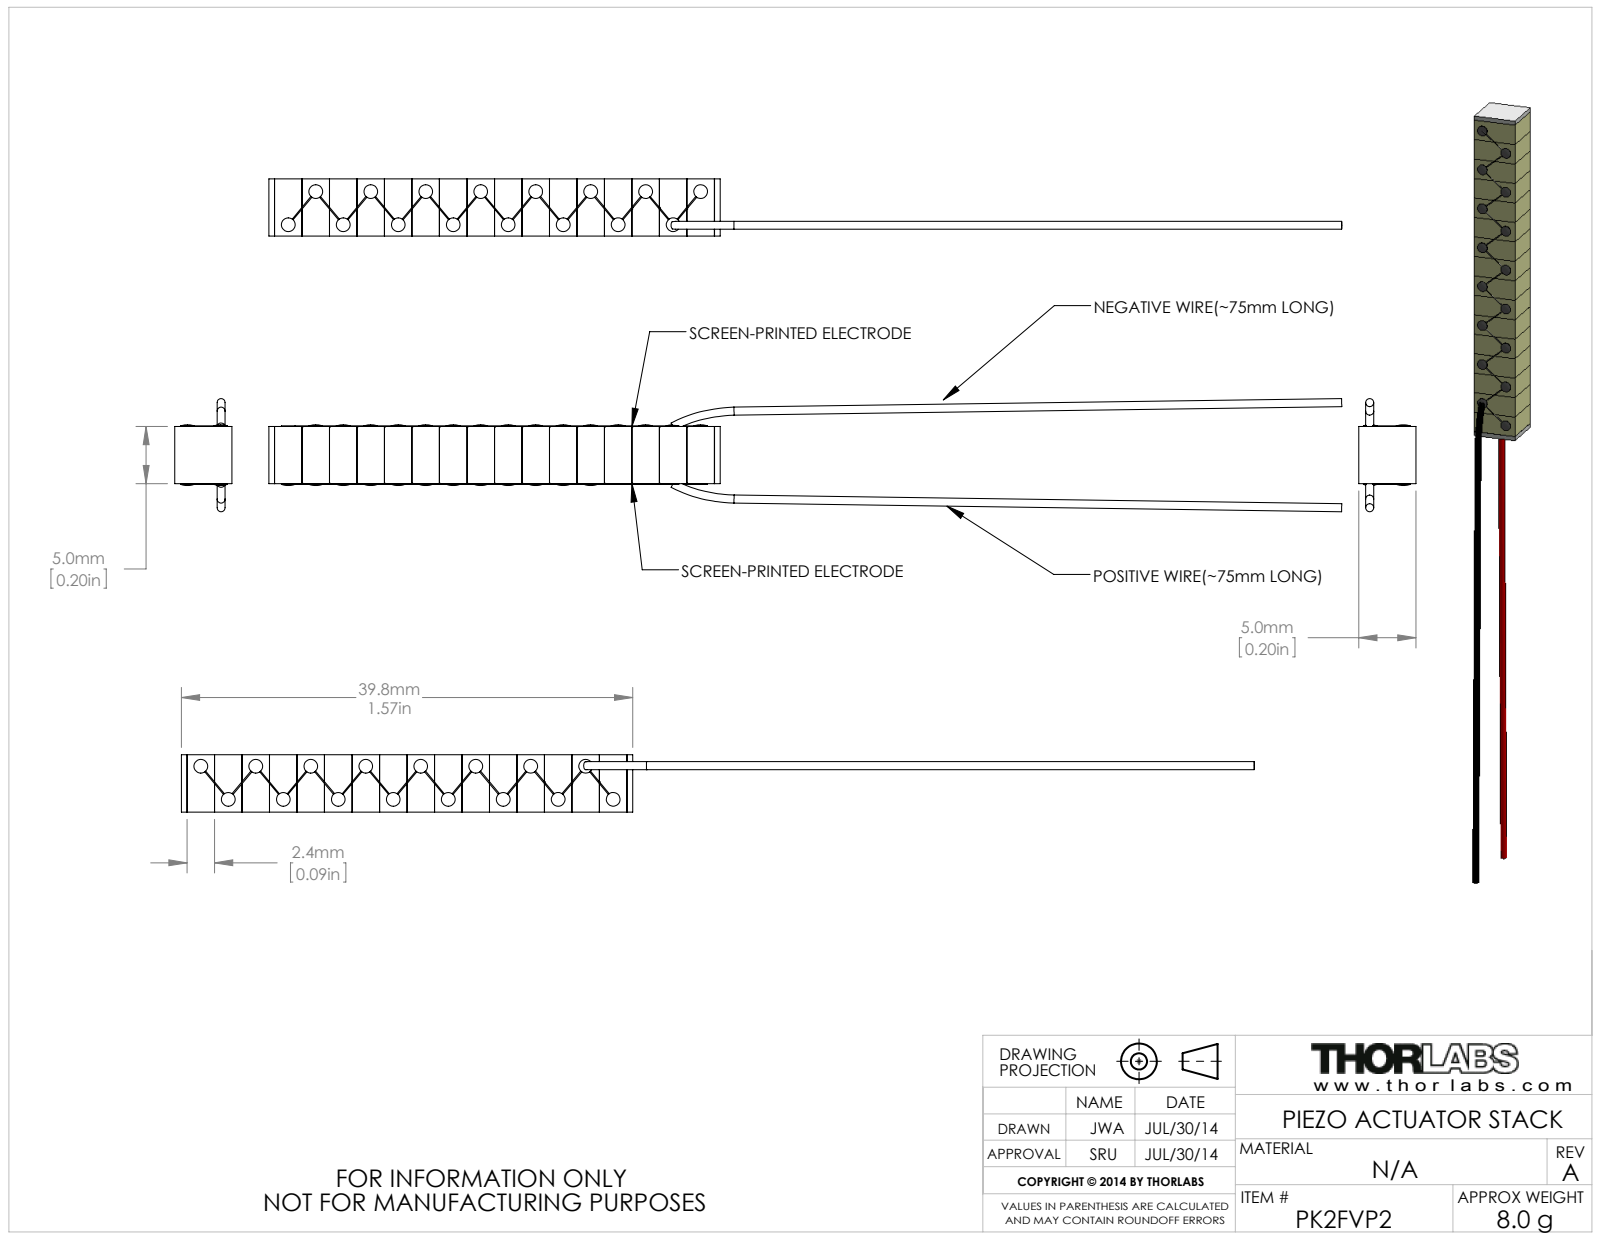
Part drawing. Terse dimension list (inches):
name: PK2FVP2
written by: SolidWorks 2012 (AUTOMOTIVE_DESIGN)
unit: in
bodies: 27 solids, 346 faces (149 planar, 138 cylindrical, 59 other)
size: 3.688 × 0.389 × 0.197
volume: 0.063 in³; area: 3.111 in²
bosses: 16× ⌀0.047, 2× ⌀0.028
face distances: 0.094, 0.189, 0.283, 0.378, 0.472, 0.567, 0.661, 0.756, 0.197, 0.85
